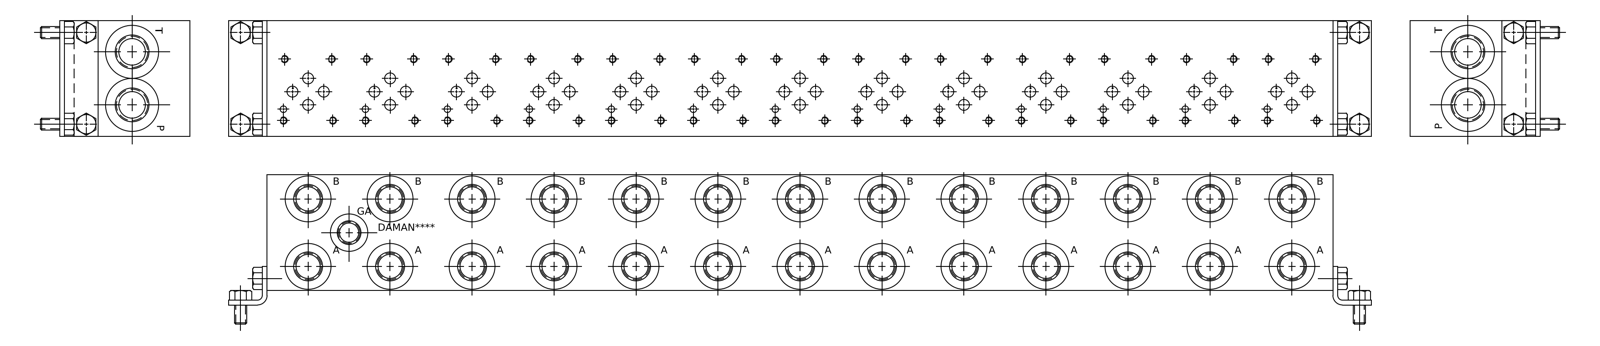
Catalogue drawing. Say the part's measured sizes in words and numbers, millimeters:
The part is named "Part_AD03P132S_3D". Its 3-D file was written by "Autodesk Inventor 2020 (AUTOMOTIVE_DESIGN)". It is 1 solid with 1633 faces: 736 planar, 335 cylindrical and 562 other. Overall it measures 701.67 by 76.2 by 76.2 millimeters. Its volume is 3 834 000 cubic millimeters and its surface area 288 226 square millimeters. Round holes: 52 of diameter 3.78, 52 of diameter 4.83, 39 of diameter 7.14, 26 of diameter 14.3, 26 of diameter 17.5, 26 of diameter 19.05, 26 of diameter 19.25, 26 of diameter 30.63, 13 of diameter 3.96, 13 of diameter 6.35, 2 of diameter 6.53, 2 of diameter 7.92. The main face-to-face distances are 76.2, 0.79, 75.41, 701.67, 15.06, 14.27, 61.14, 700.88, 700.89, 700.1. The hole center spacings are 107.95, 215.9, 323.85, 116.74, 431.8, 53.97, 53.98, 220.43.
